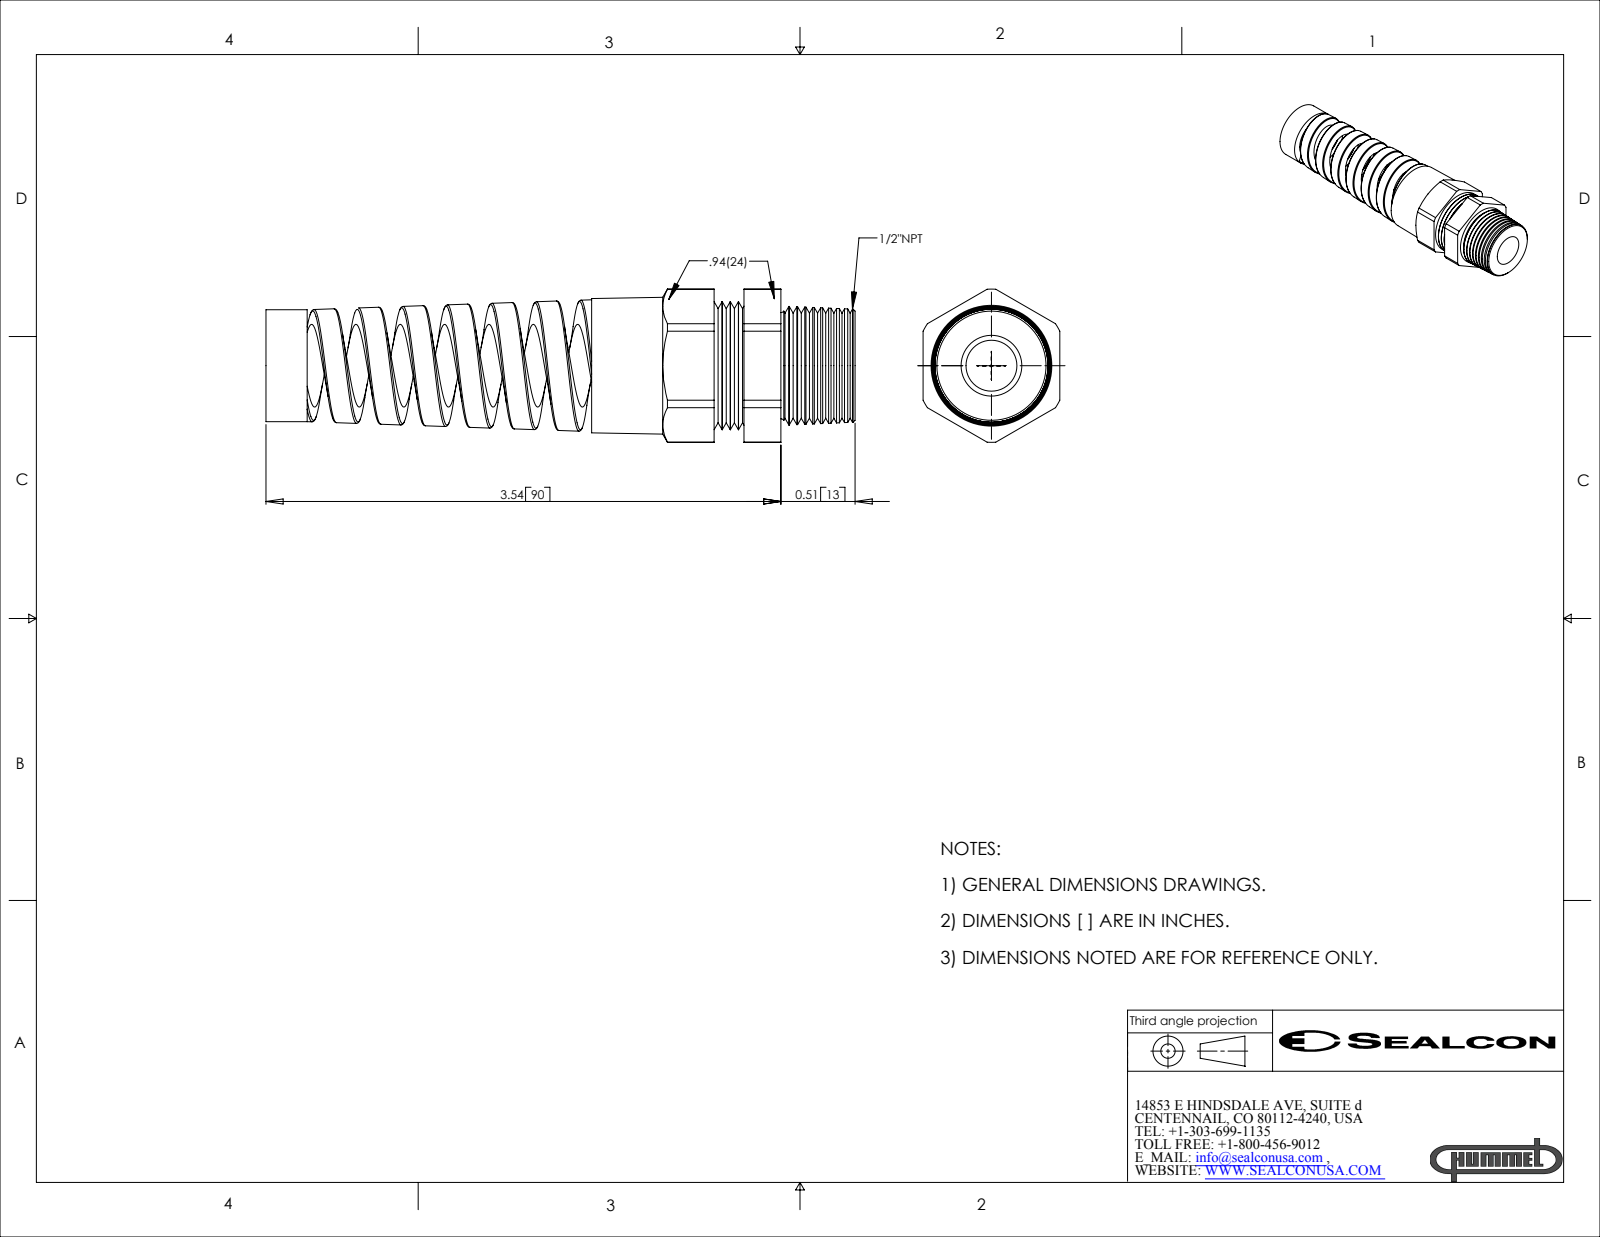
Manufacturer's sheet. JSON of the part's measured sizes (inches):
{"part_name": "CF13NR-GY", "step_written_by": "SolidWorks 2007 (CONFIG_CONTROL_DESIGN)", "units": "inches", "bodies": {"solids": 1, "faces": 164, "planar": 19, "cylindrical": 39, "other": 106}, "overall_size": [4.05, 1.053, 0.94], "volume_in3": 1.323, "surface_area_in2": 20.17, "round_holes": [[0.35, 1], [0.569, 1]], "round_bosses_or_shafts": [[0.88, 1], [0.769, 1]], "partial_cylinders_radius": [[0.526, 1]], "face_to_face_distances": [0.94, 1.811, 1.301, 0.51, 2.239, 3.54, 4.05, 3.287, 1.048, 0.254]}
